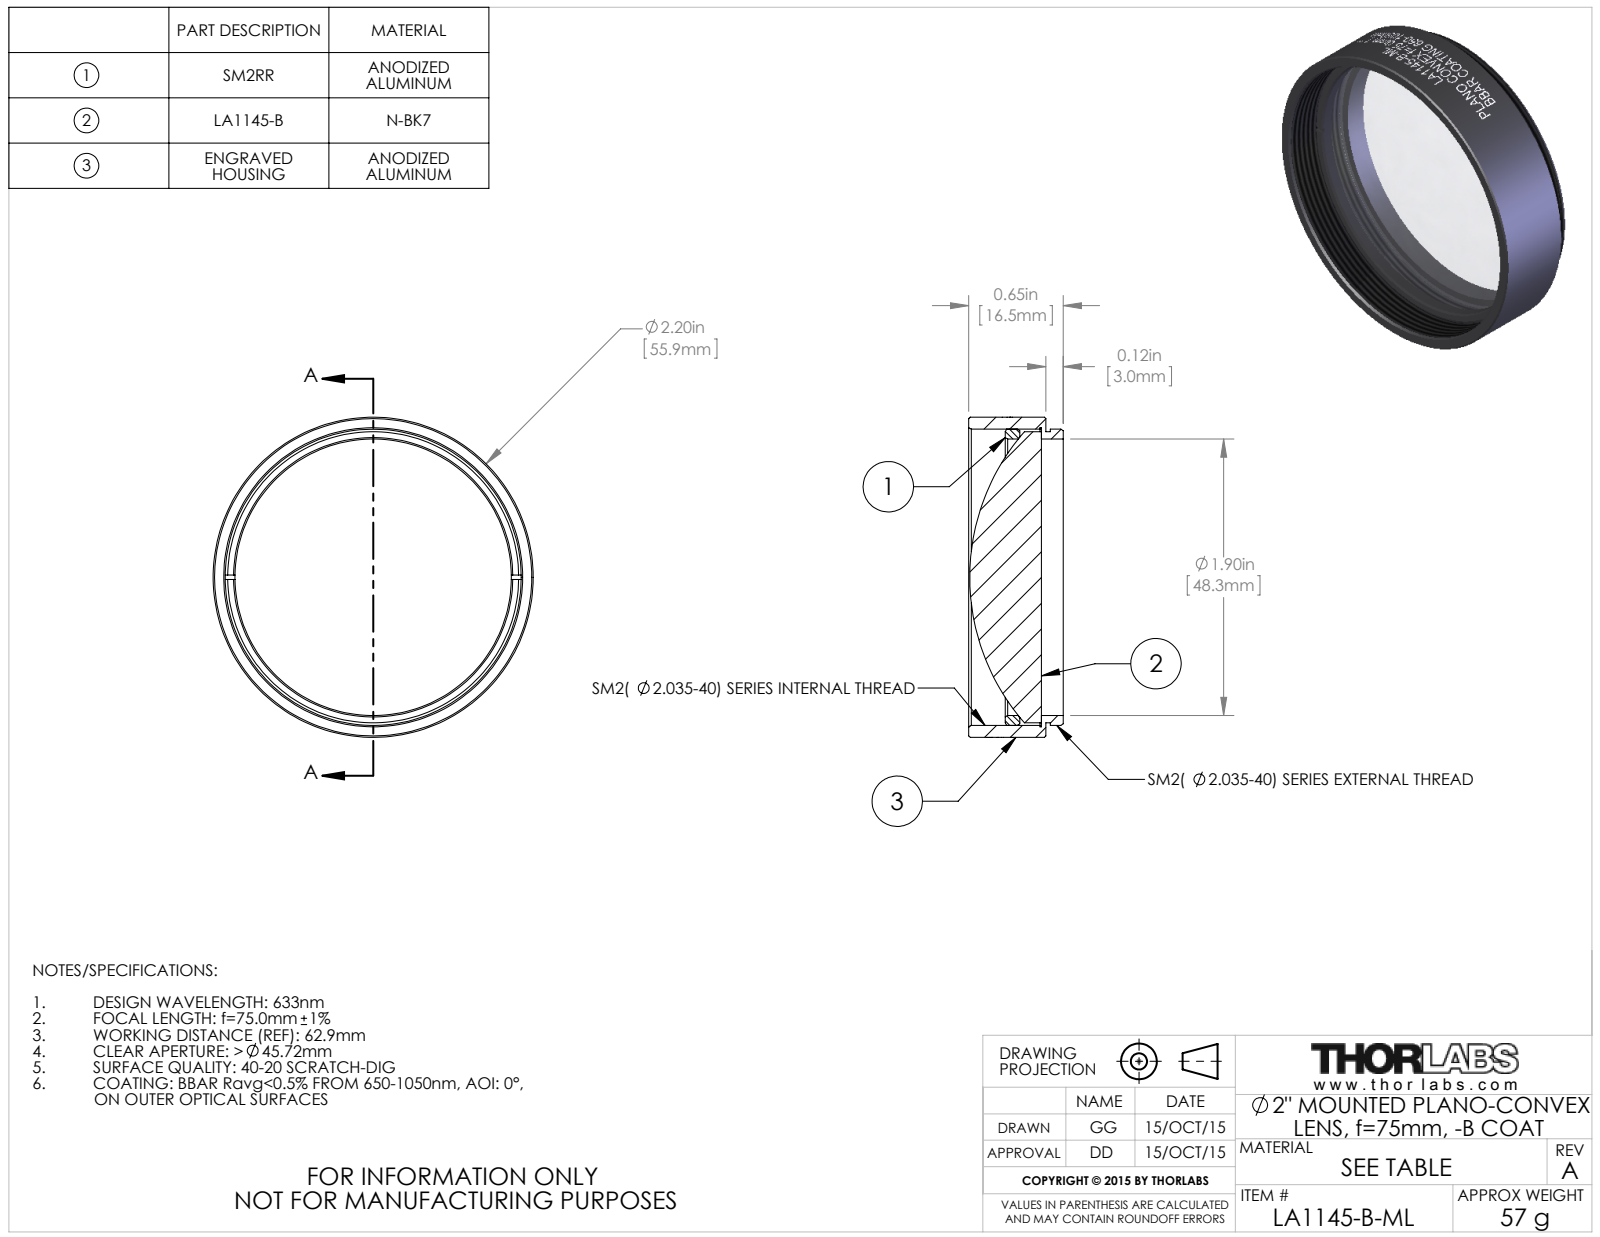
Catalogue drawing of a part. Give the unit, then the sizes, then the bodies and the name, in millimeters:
Units: millimetres
Overall size (bounding box): 55.9 × 55.9 × 16.5
Round holes (diameter × count): ⌀48.3 ×1, ⌀52.2 ×1
Round bosses / shafts (diameter × count): ⌀55.9 ×1, ⌀51.7 ×1, ⌀50.8 ×1, ⌀50.8 ×1
Main face-to-face distances: 0.8, 12.7, 13.5, 16.5, 3.8, 3, 8.9, 3.8, 4.6, 7.6
Volume: 22 520 mm³ · Surface area: 12 900 mm²
Bodies: 3 solids, 144 faces (16 planar, 108 cylindrical, 20 other)
Part name (STEP PRODUCT): TTN039514-E0W
STEP written by: SolidWorks 2014 (CONFIG_CONTROL_DESIGN)
